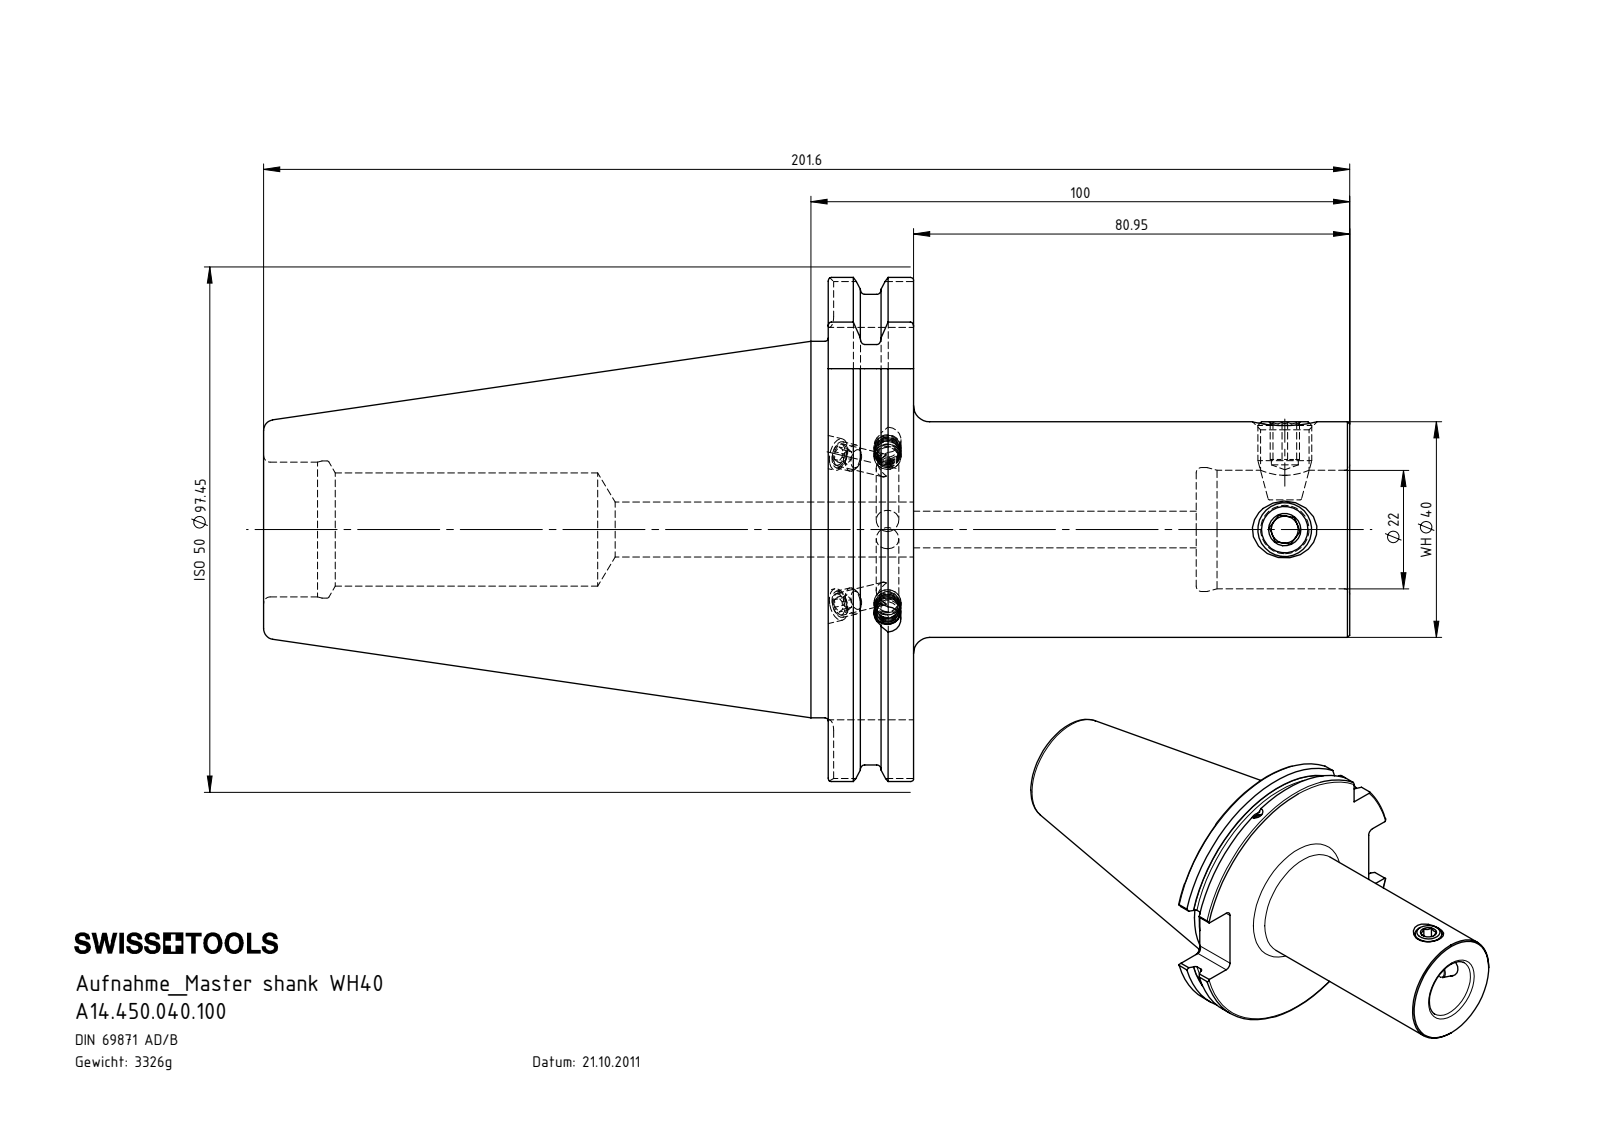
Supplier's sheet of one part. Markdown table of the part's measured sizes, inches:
| quantity | value |
| --- | --- |
| part name | SB5-WH4.K01.100_B; WH4-ER1.001.015; A14.450.040.100; ISO 4026 - M5 x 4_PreviewCfg (+1 more) |
| STEP written by | SolidWorks 2022 (CONFIG_CONTROL_DESIGN) |
| units | inches |
| bodies | 9 solids, 308 faces (85 planar, 79 cylindrical, 144 other) |
| overall size | 7.937 × 3.837 × 3.681 |
| volume | 25.85 in³ |
| surface area | 89.87 in² |
| round holes (diameter × count) | 0.165 × 3, 0.197 × 3, 0.157 × 2, 0.236 × 2, 0.354 × 2, 0.268 × 1, 0.402 × 1, 0.827 × 1, 0.866 × 1, 0.906 × 1, 0.984 × 1, 1.002 × 1 |
| round bosses / shafts (diameter × count) | 0.197 × 3, 0.394 × 2, 3.583 × 1, 2.75 × 1, 1.575 × 1 |
| partial cylindrical surfaces (radius × count) | 0.079 × 8, 1.919 × 1 |
| main face-to-face distances | 0.624, 3.811, 3.187, 4.126, 4.75, 7.937, 2.866, 6.815, 2.689, 2.065 |
